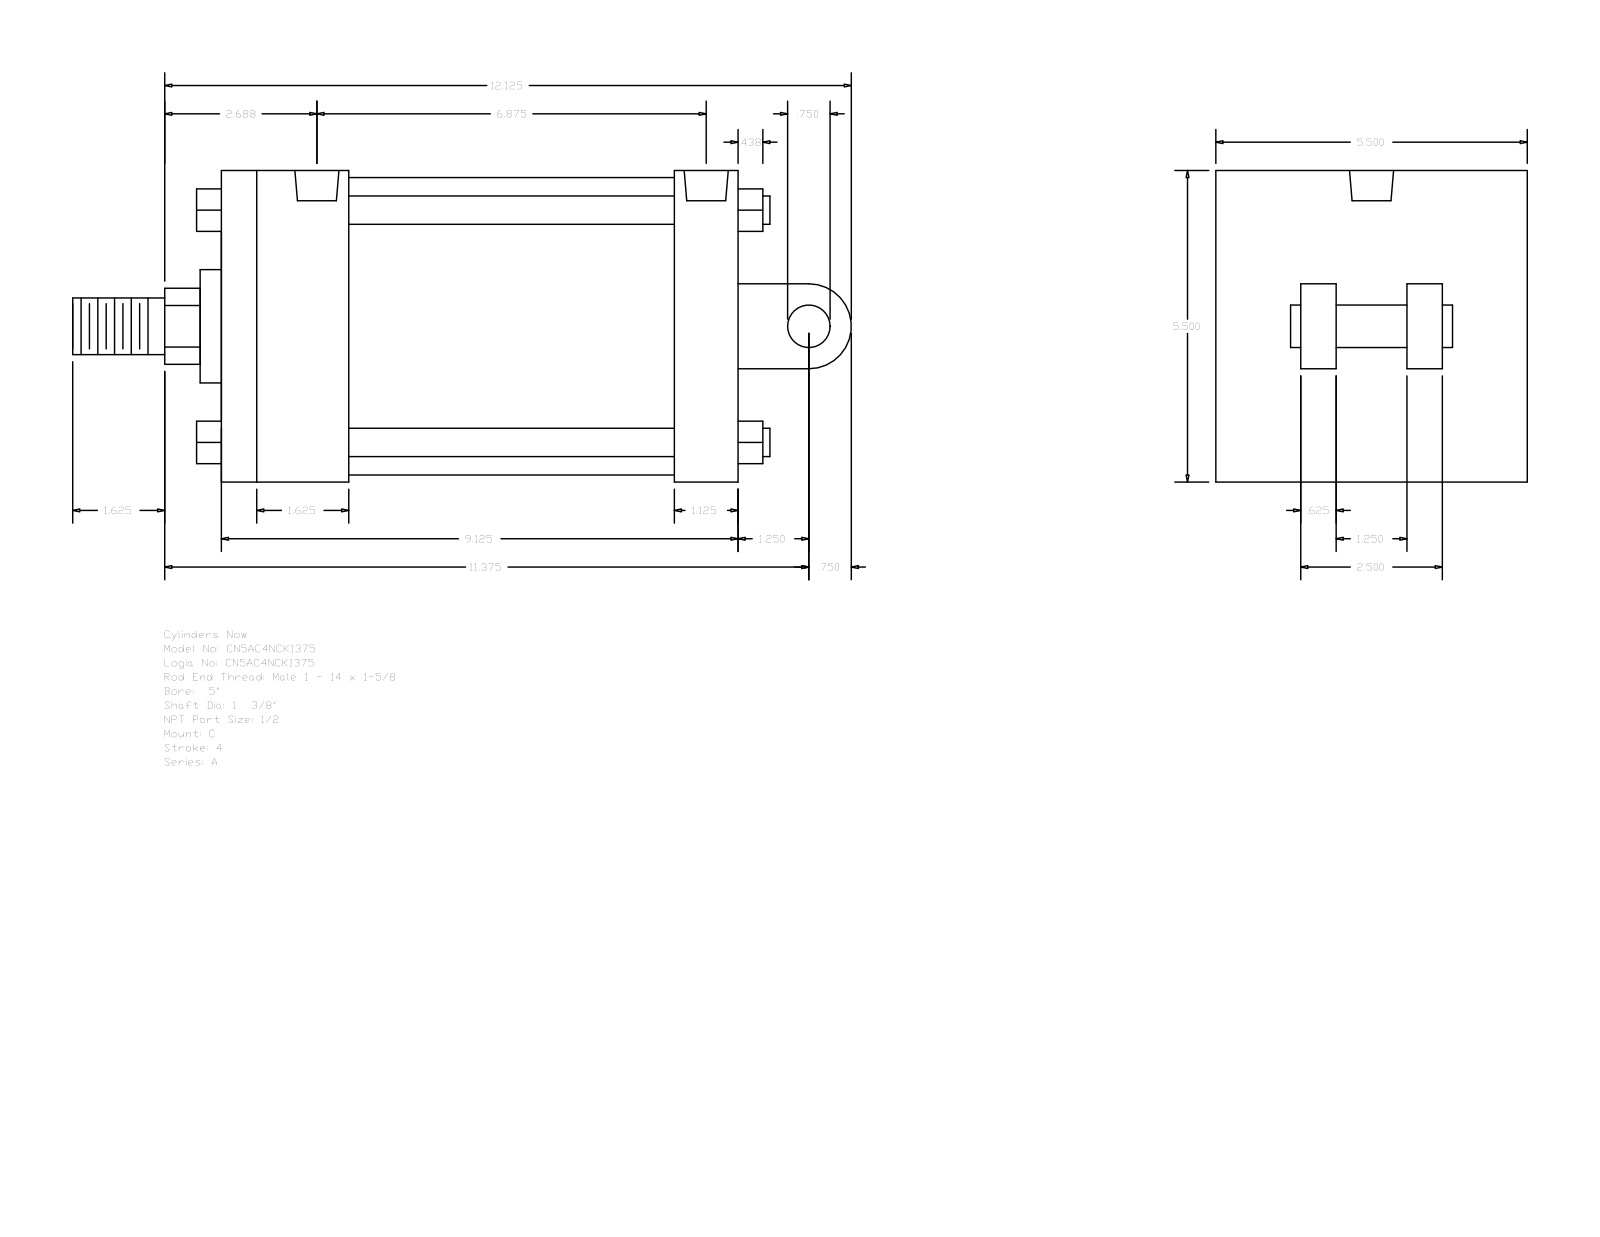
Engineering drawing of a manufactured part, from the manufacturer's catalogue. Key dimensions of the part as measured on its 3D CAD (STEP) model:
Part name (STEP PRODUCT): A_C__0500_1.375
STEP written by: GSSL Pune (CONFIG_CONTROL_DESIGN)
Units: millimetres
Bodies: 0 solids, 135 faces (102 planar, 33 cylindrical, 0 other)
Overall size (bounding box): 349.25 × 139.7 × 139.7
Round holes (diameter × count): ⌀8.73 ×4, ⌀19.77 ×2
Round bosses / shafts (diameter × count): ⌀12.7 ×4, ⌀133.35 ×1, ⌀50.8 ×1, ⌀34.92 ×1, ⌀25.4 ×1, ⌀19.05 ×1
Partial cylindrical surfaces — rounded edges, fillets, slot ends (radius × count): R17.06 ×1, R19.05 ×1
Main face-to-face distances: 139.7, 231.78, 57.15, 28.58, 203.2, 146.05, 174.63, 38.1, 53.97, 101.6
Hole centre spacings: 2.39, 169.85, 172.24, 174.63
